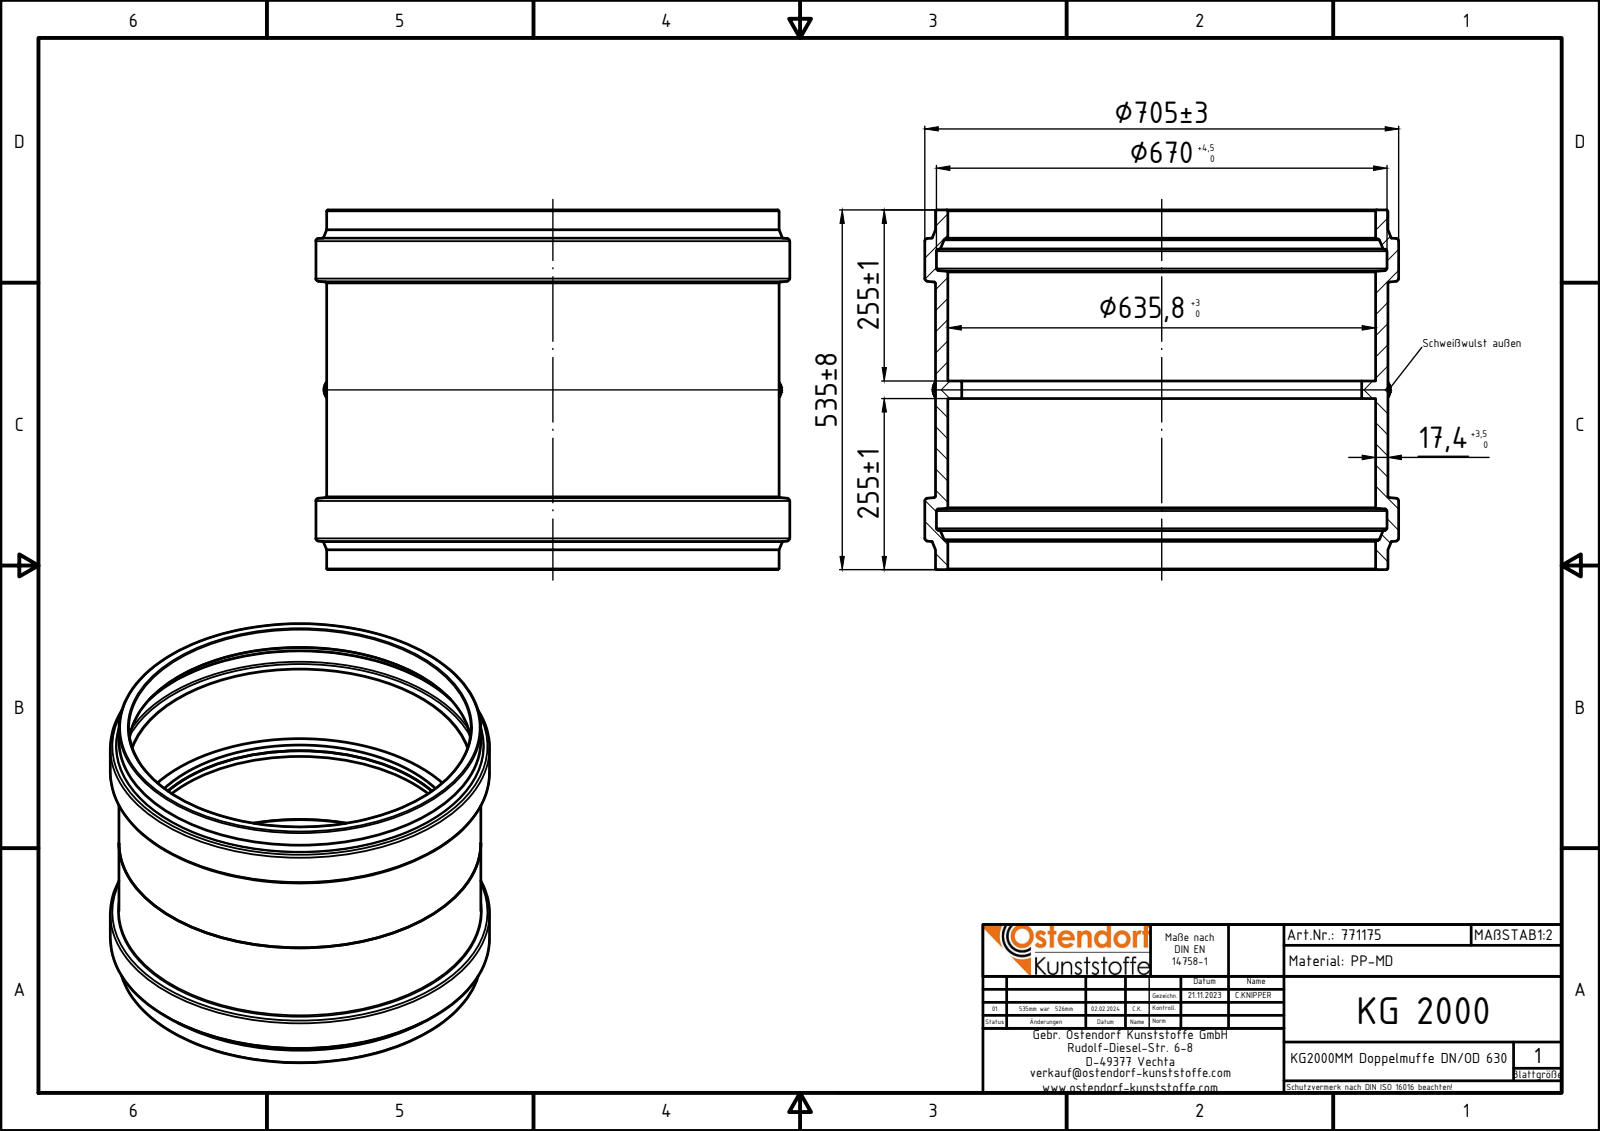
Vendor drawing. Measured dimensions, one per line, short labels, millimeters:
name: 771175z
written by: Autodesk Inventor 2024 (AUTOMOTIVE_DESIGN)
unit: mm
bodies: 2 solids, 58 faces (6 planar, 14 cylindrical, 38 other)
size: 704.8 × 704.8 × 535
volume: 23 090 000 mm³; area: 2 712 000 mm²
holes: 1× ⌀594.8, 1× ⌀635.8, 1× ⌀670
bosses: 1× ⌀704.8, 1× ⌀672.6
face distances: 13, 254.5, 267.5, 280.5, 26, 535
